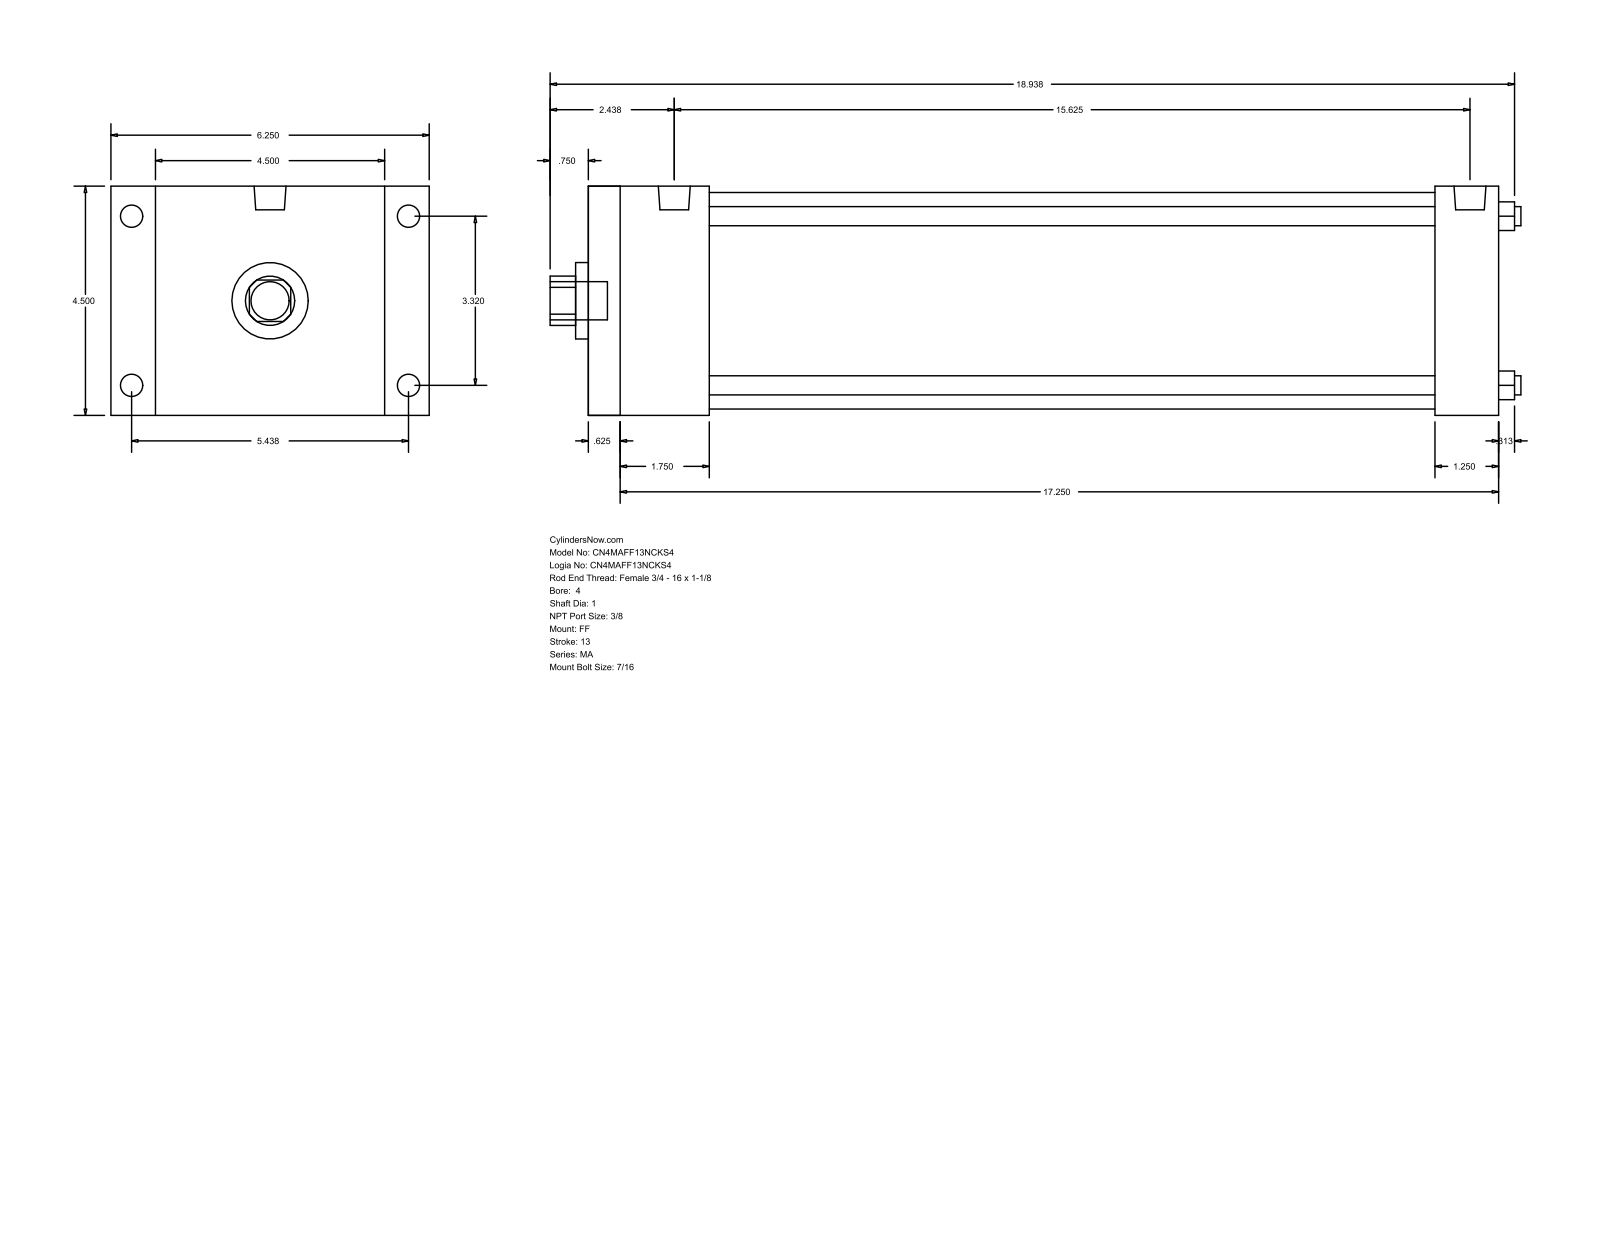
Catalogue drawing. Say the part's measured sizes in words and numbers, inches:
The part is named "MA_FF__0400_1". Its 3-D file was written by "GSSL Pune (CONFIG_CONTROL_DESIGN)". It is 0 solids with 92 faces: 64 planar, 28 cylindrical and 0 other. Overall it measures 19.063 by 6.25 by 4.5 inches. Round holes: 4 of diameter 0.375, 1 of diameter 1, 1 of diameter 1.5, 1 of diameter 4.25. Round bosses or shafts: 8 of diameter 0.437, 2 of diameter 0.627, 1 of diameter 0.75. Partial cylindrical surfaces (rounded edges, fillets, slot ends): 1 of radius 0.484. The main face-to-face distances are 4.5, 17.875, 0.625, 17.25, 0.875, 5.375, 16.625, 16, 1.25, 2.375. The hole center spacings are 2.347, 3.32, 4.695.
